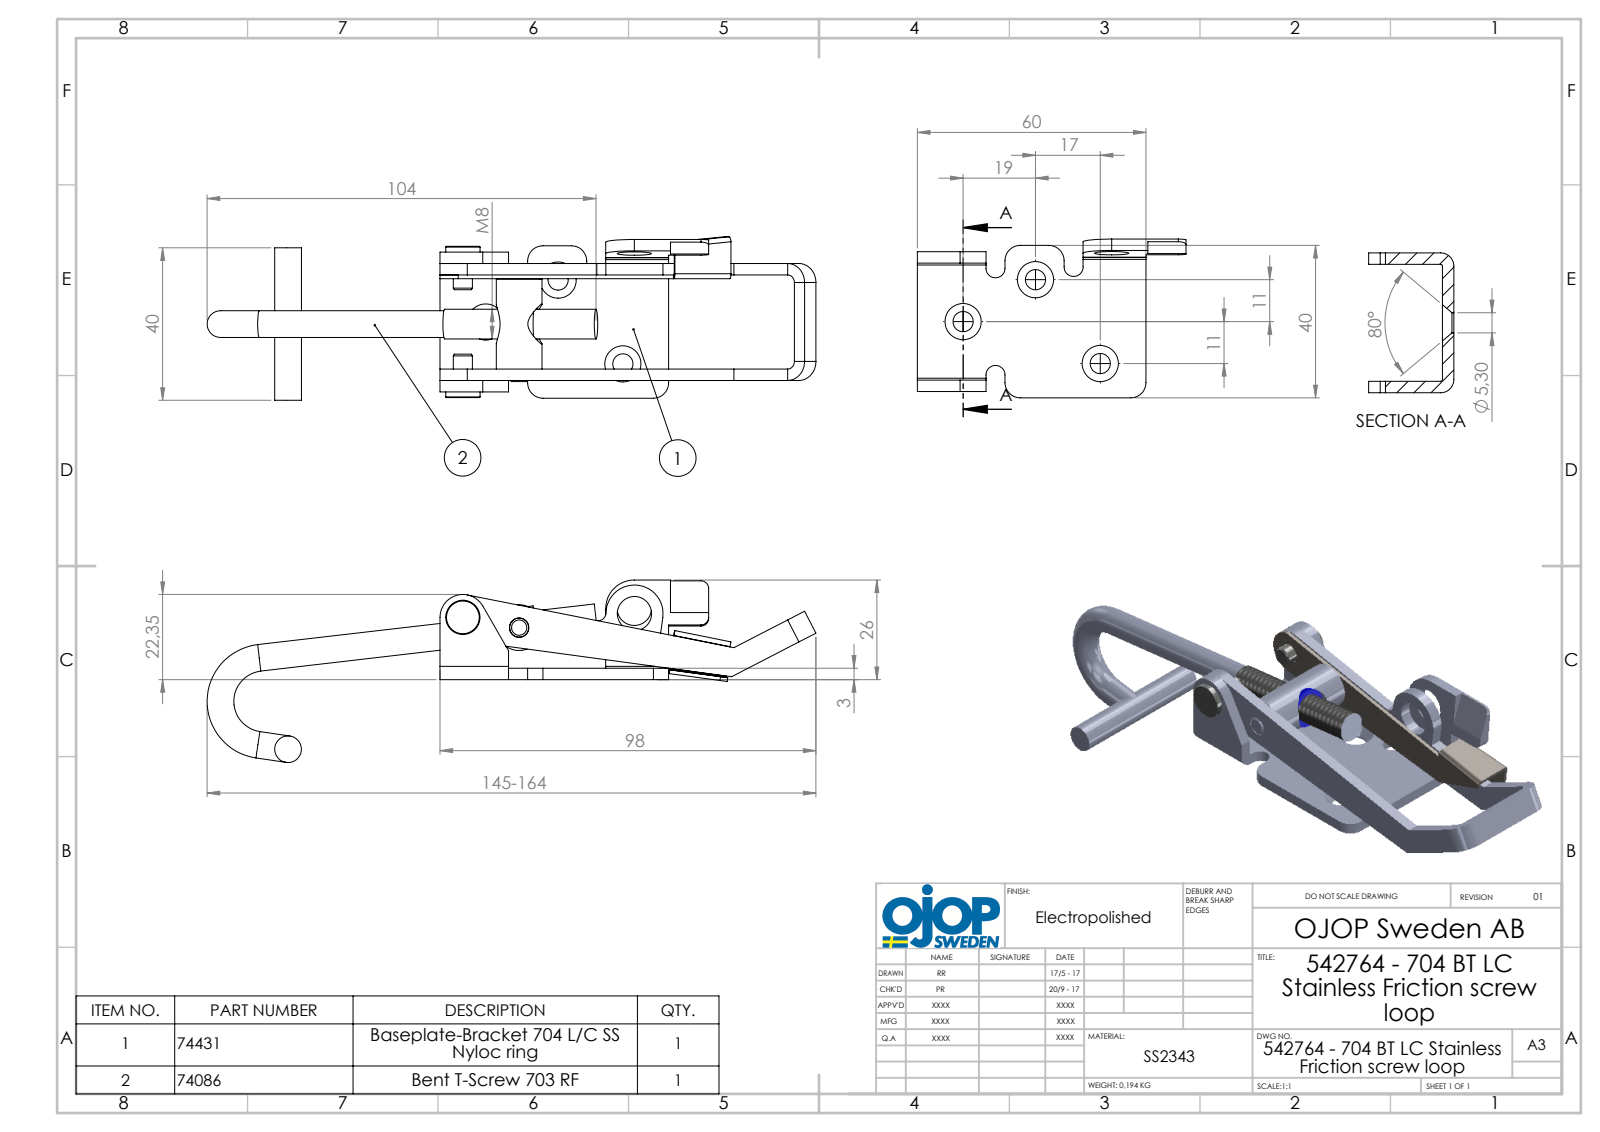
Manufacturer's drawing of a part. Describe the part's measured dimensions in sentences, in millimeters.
The part is named "703 - Rulle RF; Friction ring Stainless; 704 - Safety Catch; 74086 - Böjd T-skruv 703 RF (+5 more)". Its 3-D file was written by "SolidWorks 2015 (AUTOMOTIVE_DESIGN)". It is 8 solids with 230 faces: 109 planar, 101 cylindrical and 20 other. Overall it measures 164.63 by 42.94 by 33.06 millimeters. Its volume is 25 503 cubic millimeters and its surface area 21 391 square millimeters. Round holes: 3 of diameter 5.3, 2 of diameter 5.1, 2 of diameter 7.2, 2 of diameter 9, 1 of diameter 5.4, 1 of diameter 6.9, 1 of diameter 10.5. Round bosses or shafts: 4 of diameter 7, 2 of diameter 5, 1 of diameter 12, 1 of diameter 9, 1 of diameter 7.8. Partial cylindrical surfaces (rounded edges, fillets, slot ends): 5 of radius 2, 4 of radius 4, 3 of radius 0.3, 3 of radius 0.5, 3 of radius 1.3, 3 of radius 2.5, 3 of radius 3.5, 2 of radius 5. The main face-to-face distances are 3, 27.7, 30.7, 24.7, 1, 26.7, 23.7, 4, 6, 33.7. The hole center spacings are 15.01, 21.95, 27.8, 30.49, 37.64, 45.05.
